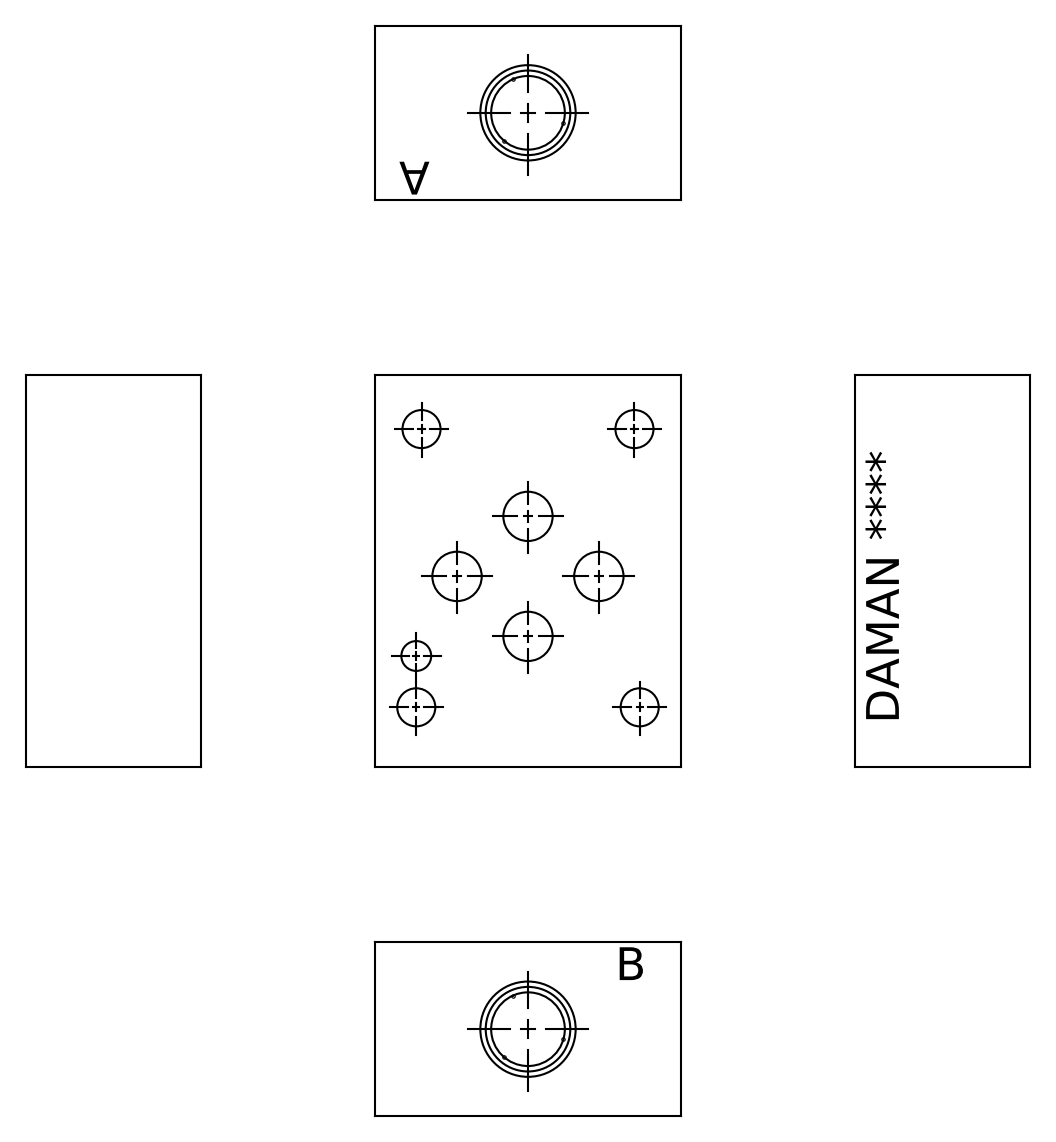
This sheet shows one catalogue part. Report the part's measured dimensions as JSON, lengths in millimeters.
{"part_name": "Part_AD03TPAB4P.B00373R4_3D", "step_written_by": "Autodesk Inventor 2022 (AUTOMOTIVE_DESIGN)", "units": "millimeters", "bodies": {"solids": 1, "faces": 413, "planar": 282, "cylindrical": 25, "other": 106}, "overall_size": [57.15, 44.45, 25.4], "volume_mm3": 56928, "surface_area_mm2": 13514, "round_holes": [[7.14, 8], [5.54, 4], [12.7, 4], [3.17, 1], [3.96, 1], [10.72, 1], [13.87, 1]], "partial_cylinders_radius": [[2.77, 3]], "face_to_face_distances": [25.4, 44.45, 57.15, 1.32, 24.08, 11.4, 45.75, 44.41, 34.35, 57.11], "hole_center_spacings": [13.52, 13.53, 16.5, 20.65, 28.99, 13, 13.54, 17.48]}
